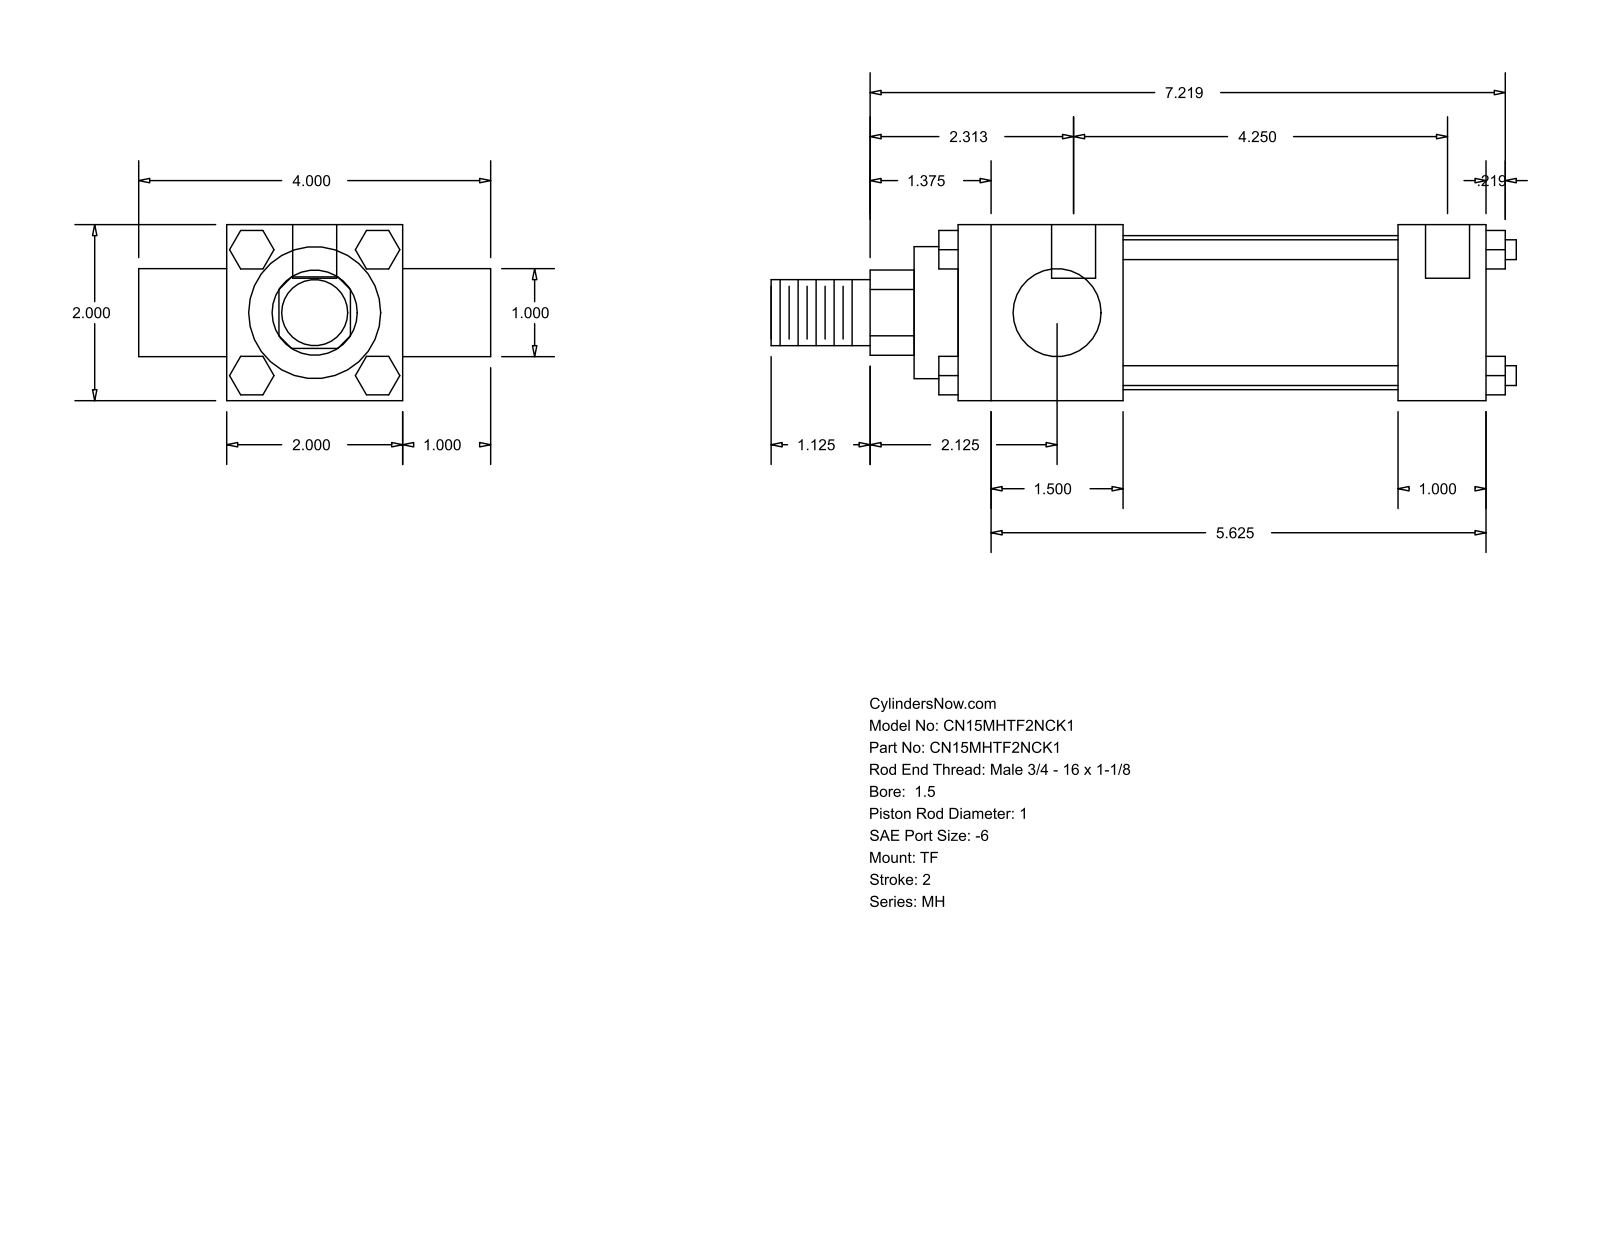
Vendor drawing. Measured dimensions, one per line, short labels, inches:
name: MH_TF__0150_1
written by: GSSL Pune (CONFIG_CONTROL_DESIGN)
unit: in
bodies: 0 solids, 120 faces (92 planar, 28 cylindrical, 0 other)
size: 8.469 × 4 × 2
holes: 3× ⌀0.219, 2× ⌀0.5
bosses: 4× ⌀0.225, 2× ⌀1, 1× ⌀1.75, 1× ⌀1.5, 1× ⌀0.75
rounds: 1× R0.484
face distances: 2, 1, 6, 3, 1.875, 4.125, 5, 3.125, 4, 0.5
hole spacings: 0.125, 4.25, 4.375
